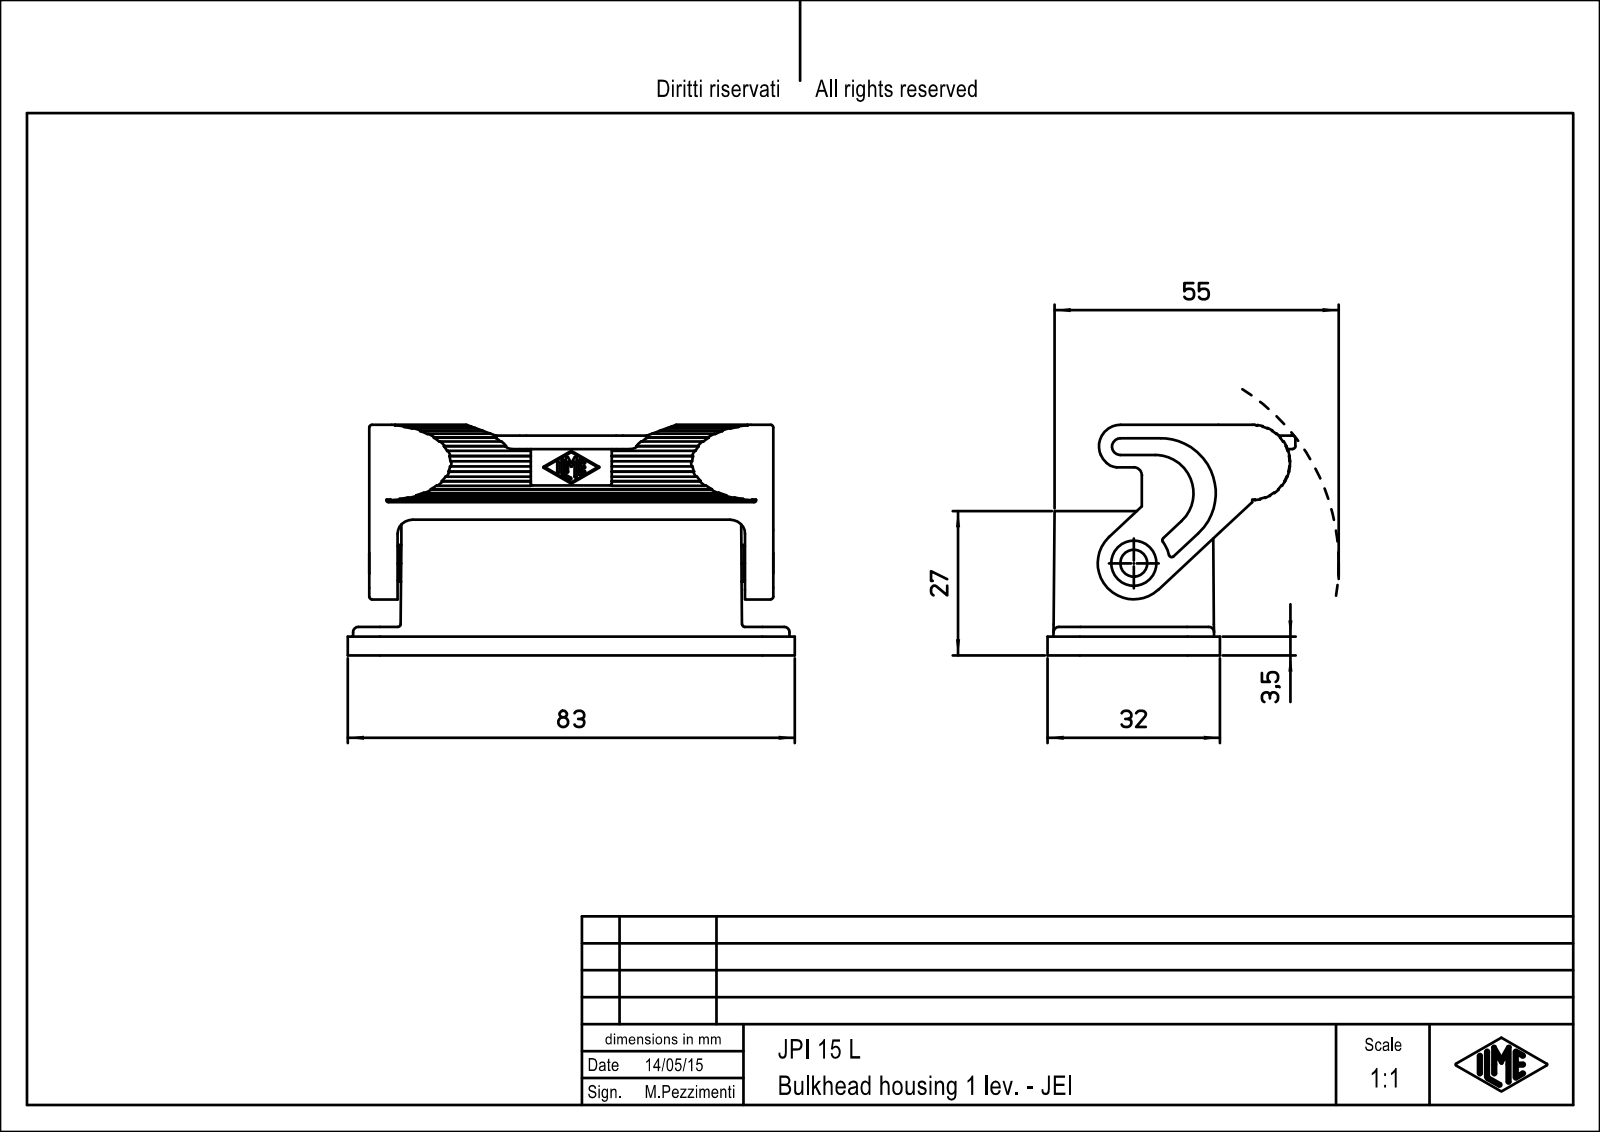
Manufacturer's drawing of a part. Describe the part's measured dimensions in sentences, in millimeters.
The part is named "CZI_15; LEVA_JP15; JPI_15_L". Its 3-D file was written by "PTC Creo Elements/Direct Modeling 19.0B 21-Mar-2015 (C) Parametric Technology GmbH (AUTOMOTIVE_DESIGN)". It is 2 solids with 441 faces: 162 planar, 213 cylindrical and 66 other. Overall it measures 83 by 46 by 42.8 millimeters. Its volume is 31 630 cubic millimeters and its surface area 20 090 square millimeters. Round holes: 4 of diameter 2.8, 4 of diameter 3, 4 of diameter 3.4, 1 of diameter 3.25, 1 of diameter 5, 1 of diameter 8.4. Round bosses or shafts: 1 of diameter 6.8, 1 of diameter 4.8, 1 of diameter 3.2. Partial cylindrical surfaces (rounded edges, fillets, slot ends): 38 of radius 0.5, 15 of radius 0.2, 7 of radius 3, 4 of radius 1, 4 of radius 2.5, 4 of radius 3.5, 4 of radius 5, 4 of radius 6. The main face-to-face distances are 23.88, 30.44, 6.56, 3.5, 5.25, 69.75, 64.5, 5.3, 4.06, 27.94. The hole center spacings are 10.28, 19.64, 59.75, 62.05, 16, 17.5, 49.5, 52.02.
